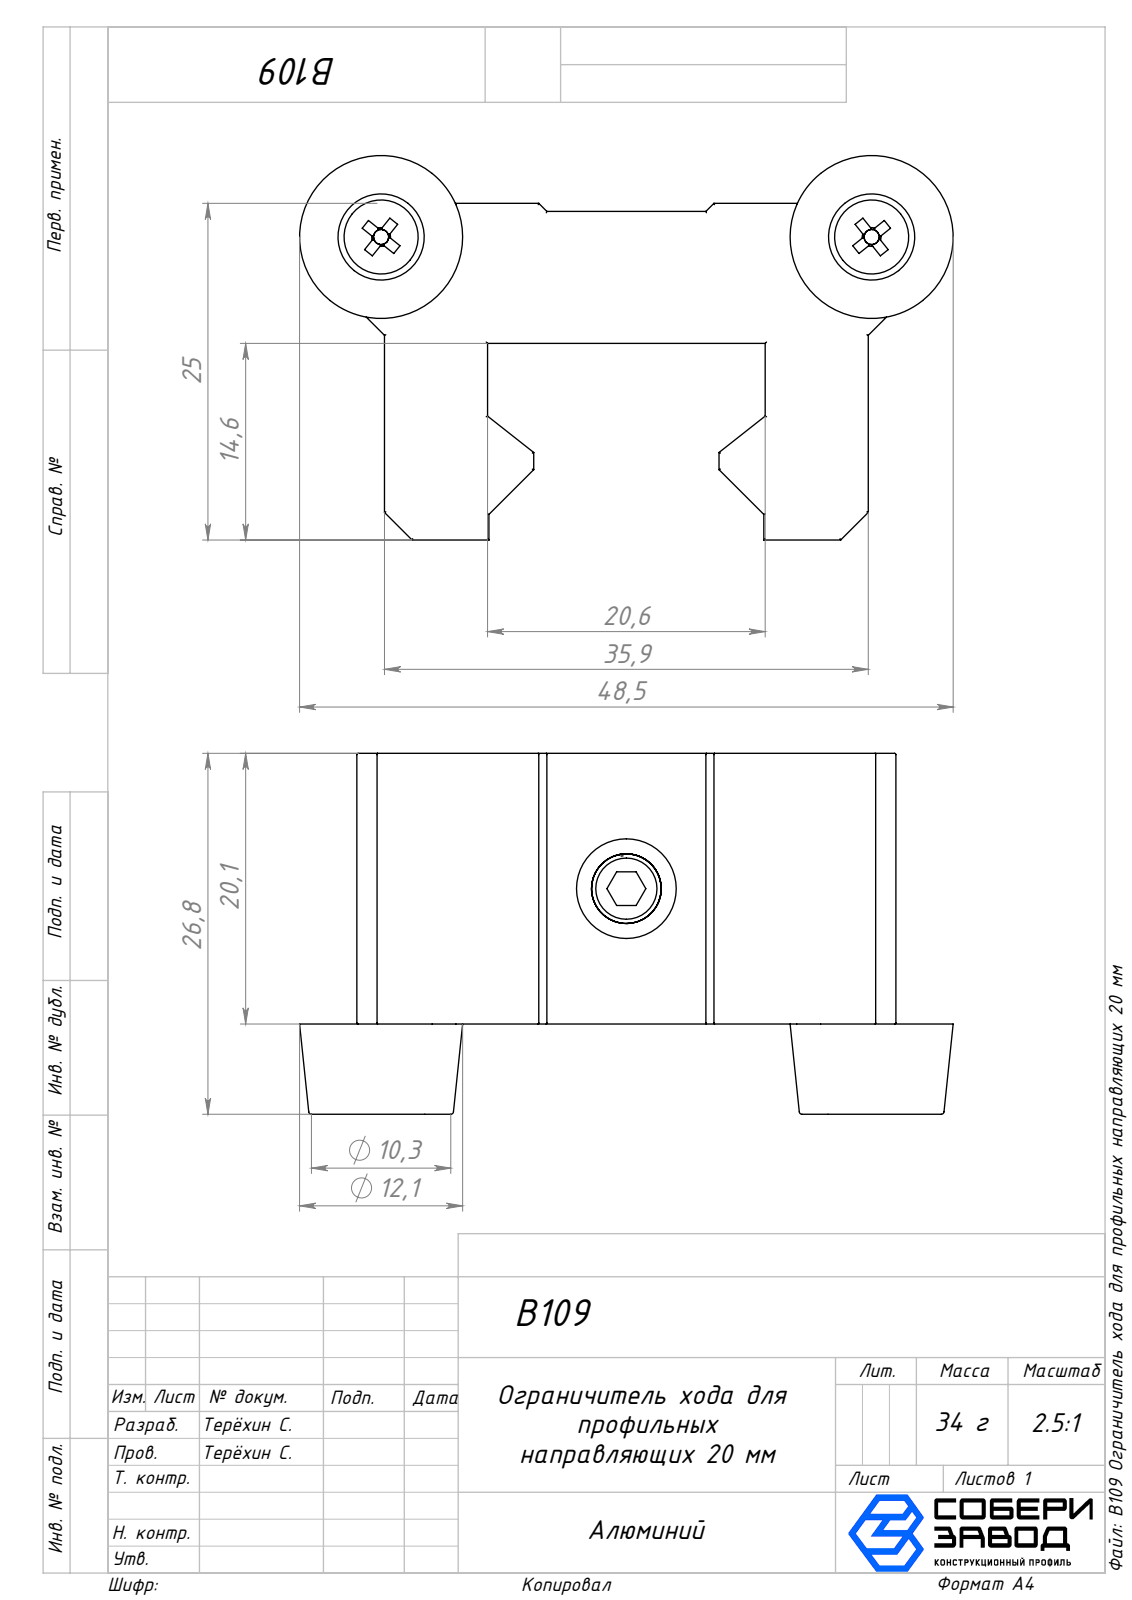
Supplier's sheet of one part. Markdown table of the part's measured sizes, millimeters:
| quantity | value |
| --- | --- |
| part name | B109 Ограничитель хода для профильных направляющих 20 мм_00; B109 Ограничитель хода для профильных направляющих 20 мм |
| STEP written by | SolidWorks 2026 (CONFIG_CONTROL_DESIGN) |
| units | millimeters |
| bodies | 1 solid, 351 faces (99 planar, 131 cylindrical, 121 other) |
| overall size | 48.5 × 28.55 × 26.8 |
| volume | 14 122 mm³ |
| surface area | 5 955 mm² |
| round holes (diameter × count) | 2.3 × 2, 3.1 × 2, 3.6 × 2, 6.4 × 2, 6 × 1 |
| round bosses / shafts (diameter × count) | 6.2 × 2, 5.5 × 2, 3 × 2 |
| partial cylindrical surfaces (radius × count) | 0.1 × 52 |
| main face-to-face distances | 20.1, 10.4, 9.8, 35.9, 2.05, 37.95, 14.6, 25, 9.7, 30.3 |
| hole center spacings | 36.4 |
